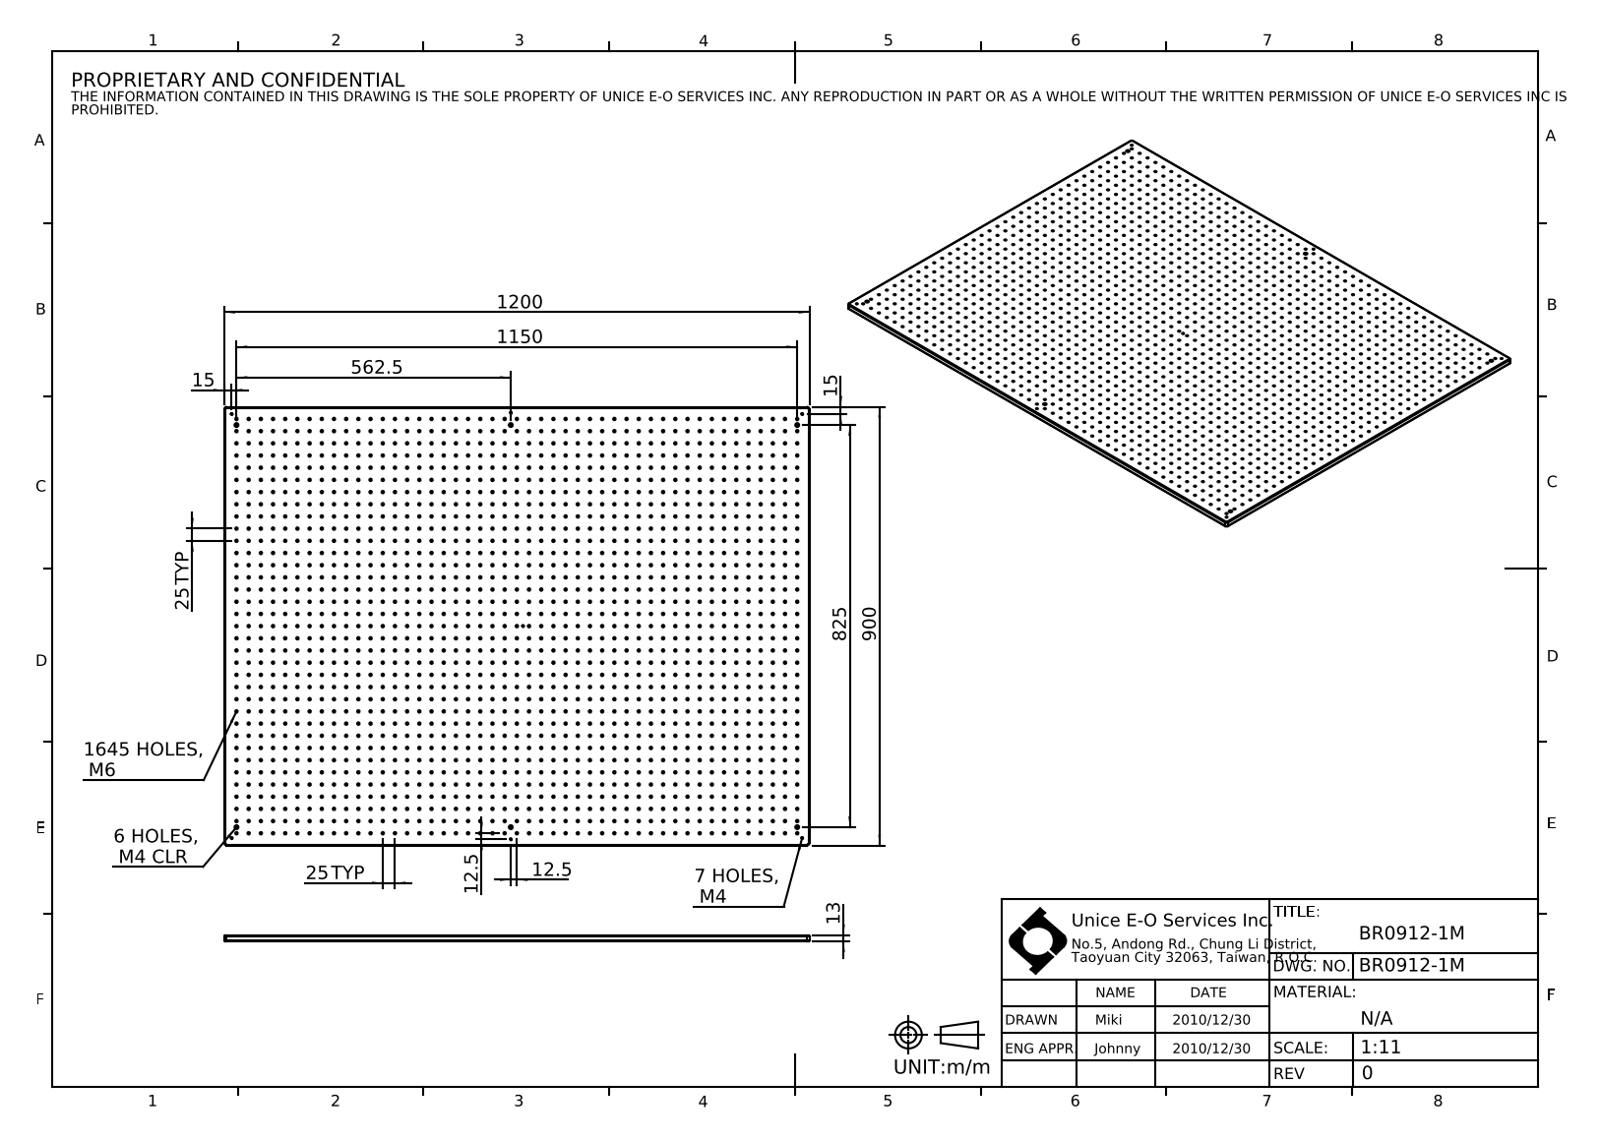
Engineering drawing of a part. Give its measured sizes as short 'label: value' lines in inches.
name: BR0912-1M
written by: SolidWorks 2016 (CONFIG_CONTROL_DESIGN)
unit: in
bodies: 1 solid, 3360 faces (12 planar, 3340 cylindrical, 8 other)
size: 47.244 × 35.433 × 0.512
volume: 830.5 in³; area: 3 846 in²
holes: 1645× ⌀0.197, 7× ⌀0.13, 6× ⌀0.177, 6× ⌀0.315
rounds: 8× R0.079, 4× R0.197
face distances: 0.512, 35.433, 47.244, 0.276, 0.236
hole spacings: 0.984, 1.969, 2.953, 3.937, 4.921, 5.906, 6.89, 7.874
